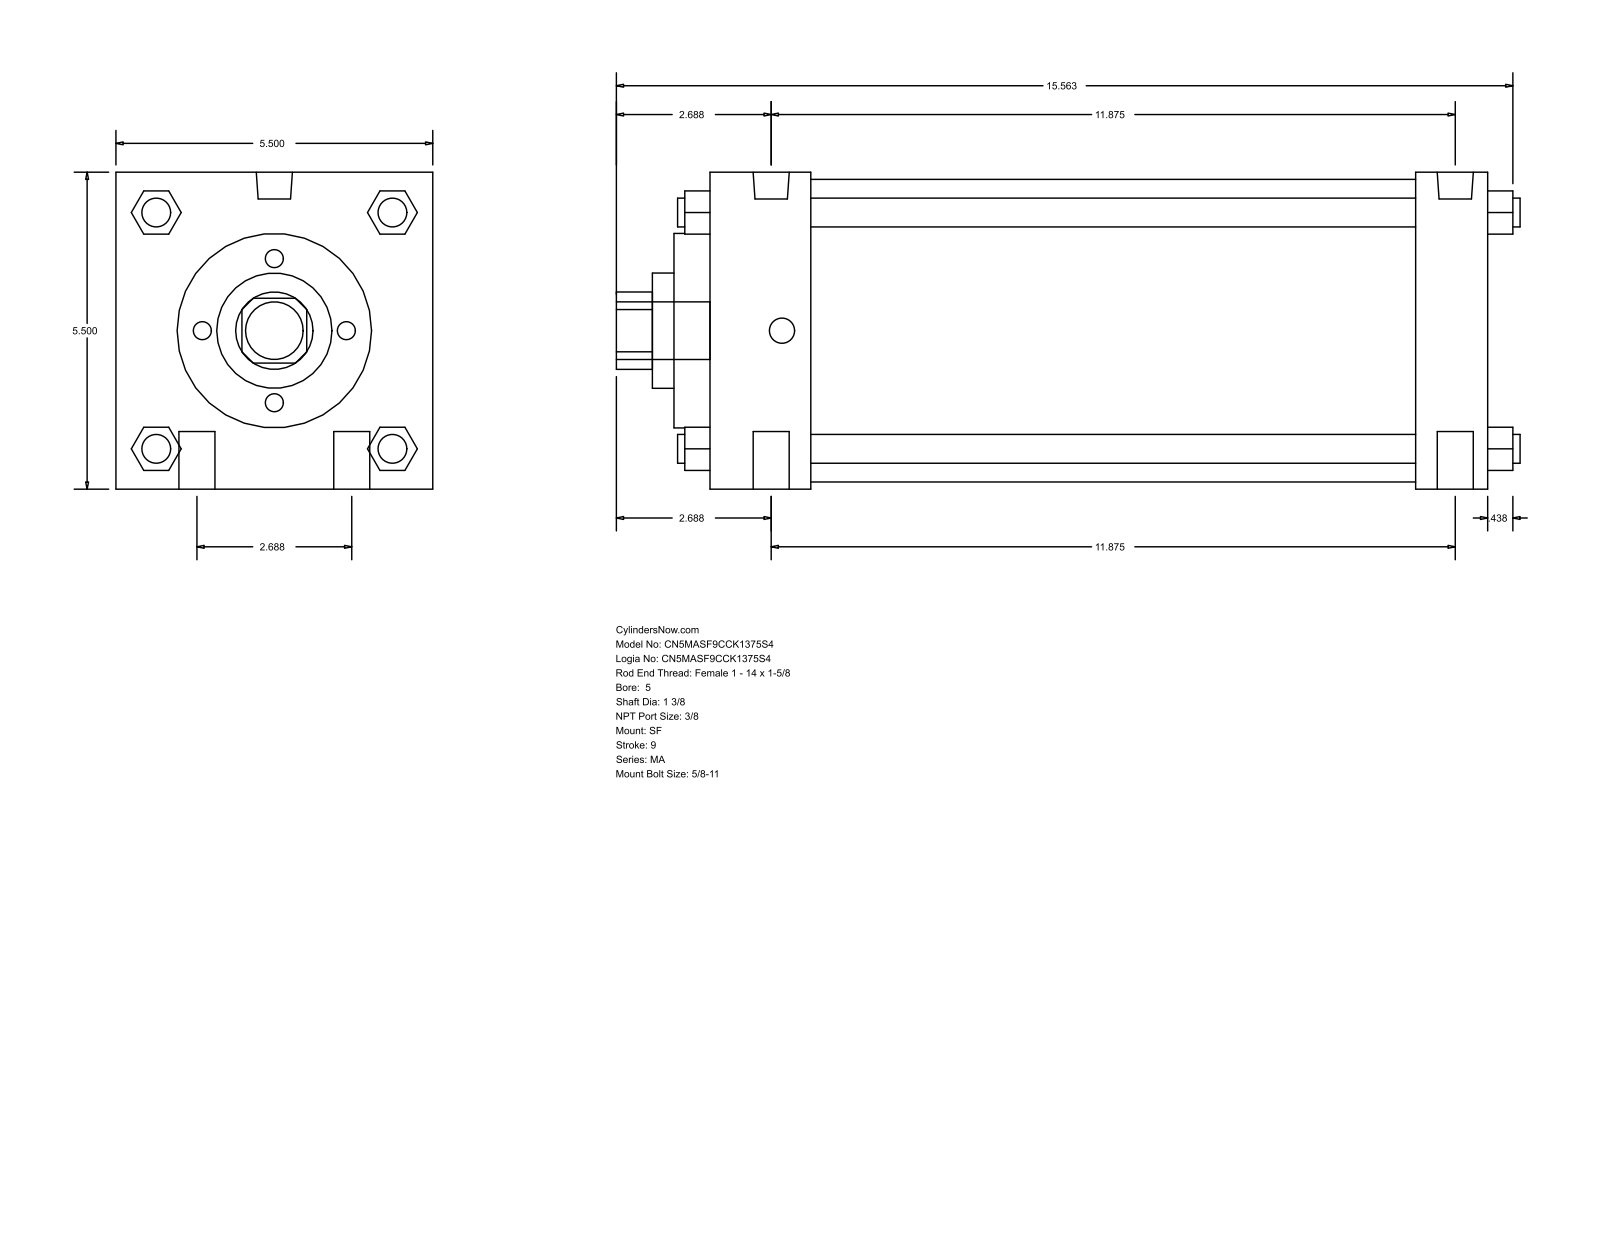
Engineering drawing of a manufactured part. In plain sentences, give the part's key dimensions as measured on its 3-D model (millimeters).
The part is named "MA_SF__0500_1.375". Its 3-D file was written by "GSSL Pune (CONFIG_CONTROL_DESIGN)". It is 0 solids with 126 faces: 95 planar, 31 cylindrical and 0 other. Overall it measures 398.46 by 139.7 by 139.7 millimeters. Round holes: 1 of diameter 34.92, 1 of diameter 50.8, 1 of diameter 85.72, 1 of diameter 133.35. Round bosses or shafts: 4 of diameter 15.88, 4 of diameter 12.7, 2 of diameter 15.93, 2 of diameter 11.11, 1 of diameter 25.4. Partial cylindrical surfaces (rounded edges, fillets, slot ends): 1 of radius 17.06. The main face-to-face distances are 139.7, 342.91, 44.45, 311.16, 266.71, 298.46, 31.75, 15.87, 60.32, 327.03.
